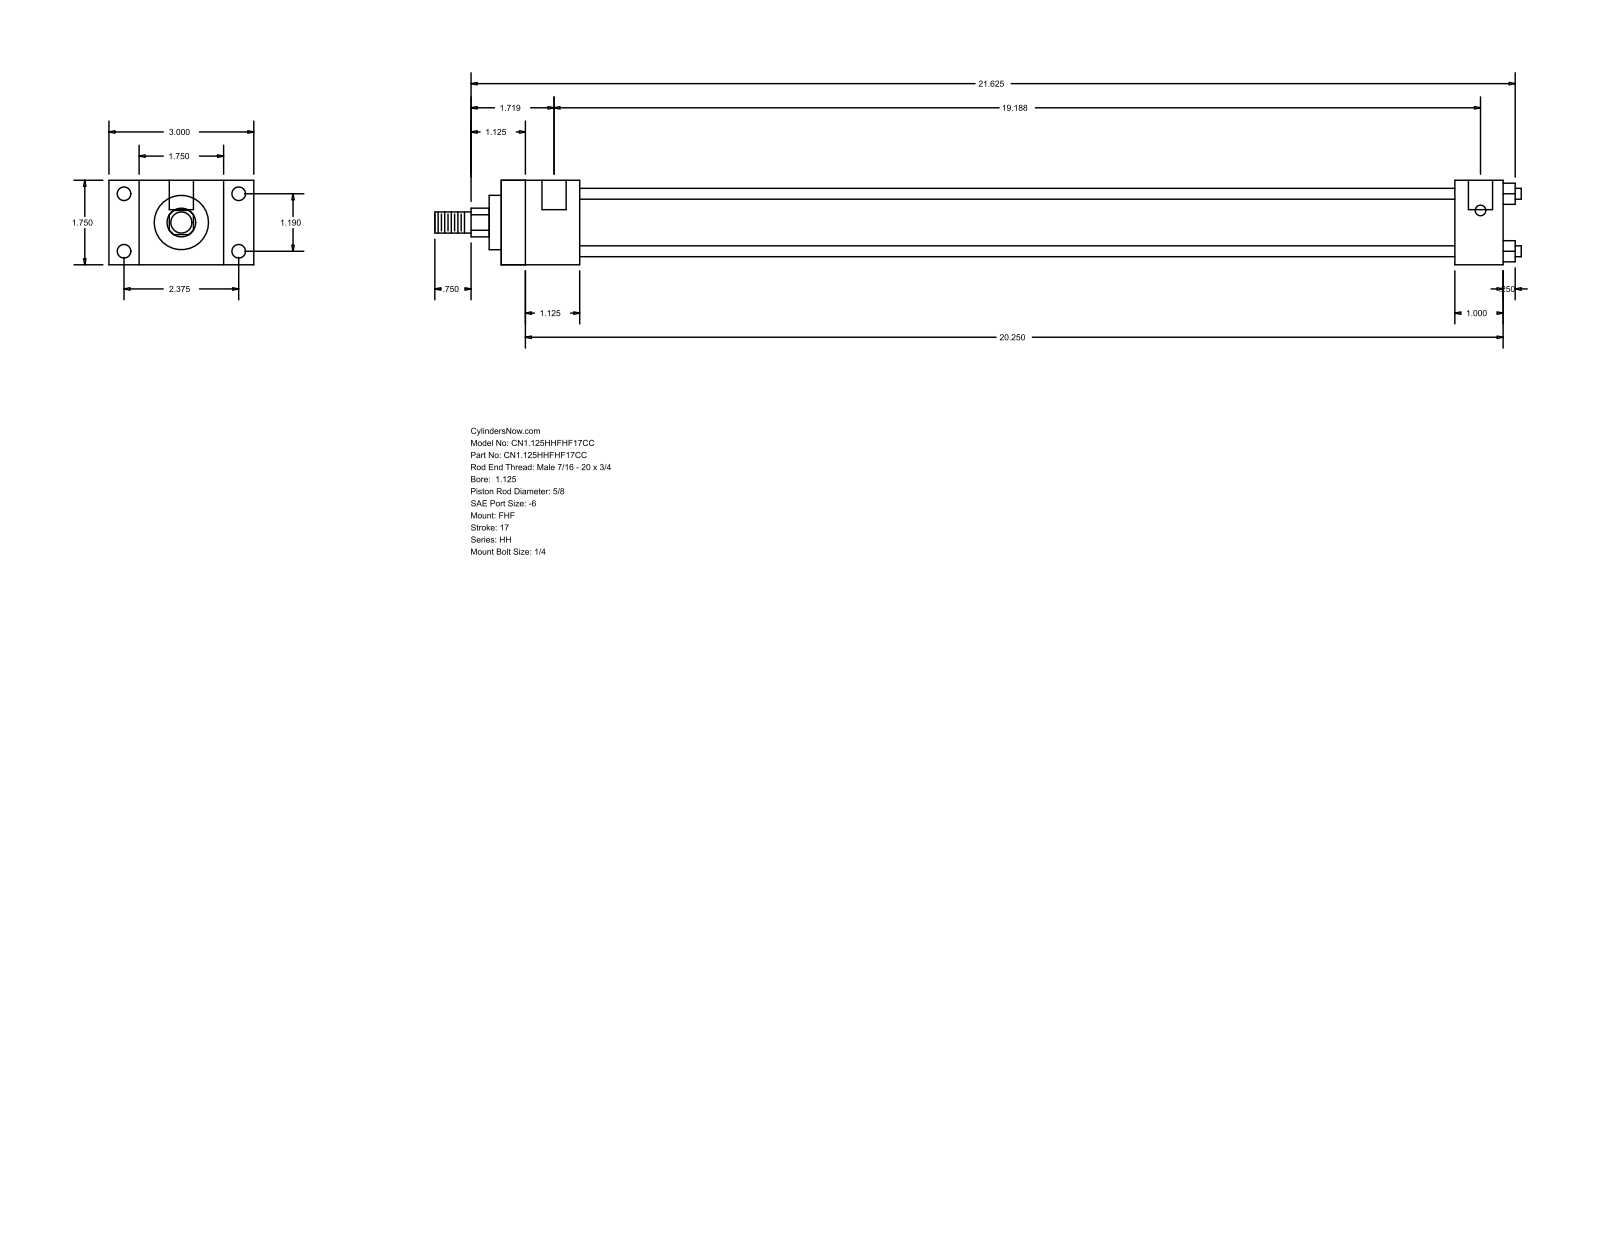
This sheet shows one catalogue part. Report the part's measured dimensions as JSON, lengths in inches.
{"part_name": "HH_FHF__0112_0.625", "step_written_by": "GSSL Pune (CONFIG_CONTROL_DESIGN)", "units": "inches", "bodies": {"solids": 0, "faces": 88, "planar": 60, "cylindrical": 28, "other": 0}, "overall_size": [22.5, 3, 1.75], "round_holes": [[0.219, 4], [0.281, 4], [0.5, 2]], "round_bosses_or_shafts": [[0.225, 4], [1.375, 1], [1.125, 1], [0.625, 1], [0.437, 1]], "partial_cylinders_radius": [[0.297, 1]], "face_to_face_distances": [1.75, 0.625, 2.375, 1.625, 3, 20.75, 19.125, 1, 19.75, 18.125], "hole_center_spacings": [1.19, 2.375, 2.656, 19.063, 0.125, 19.187]}
